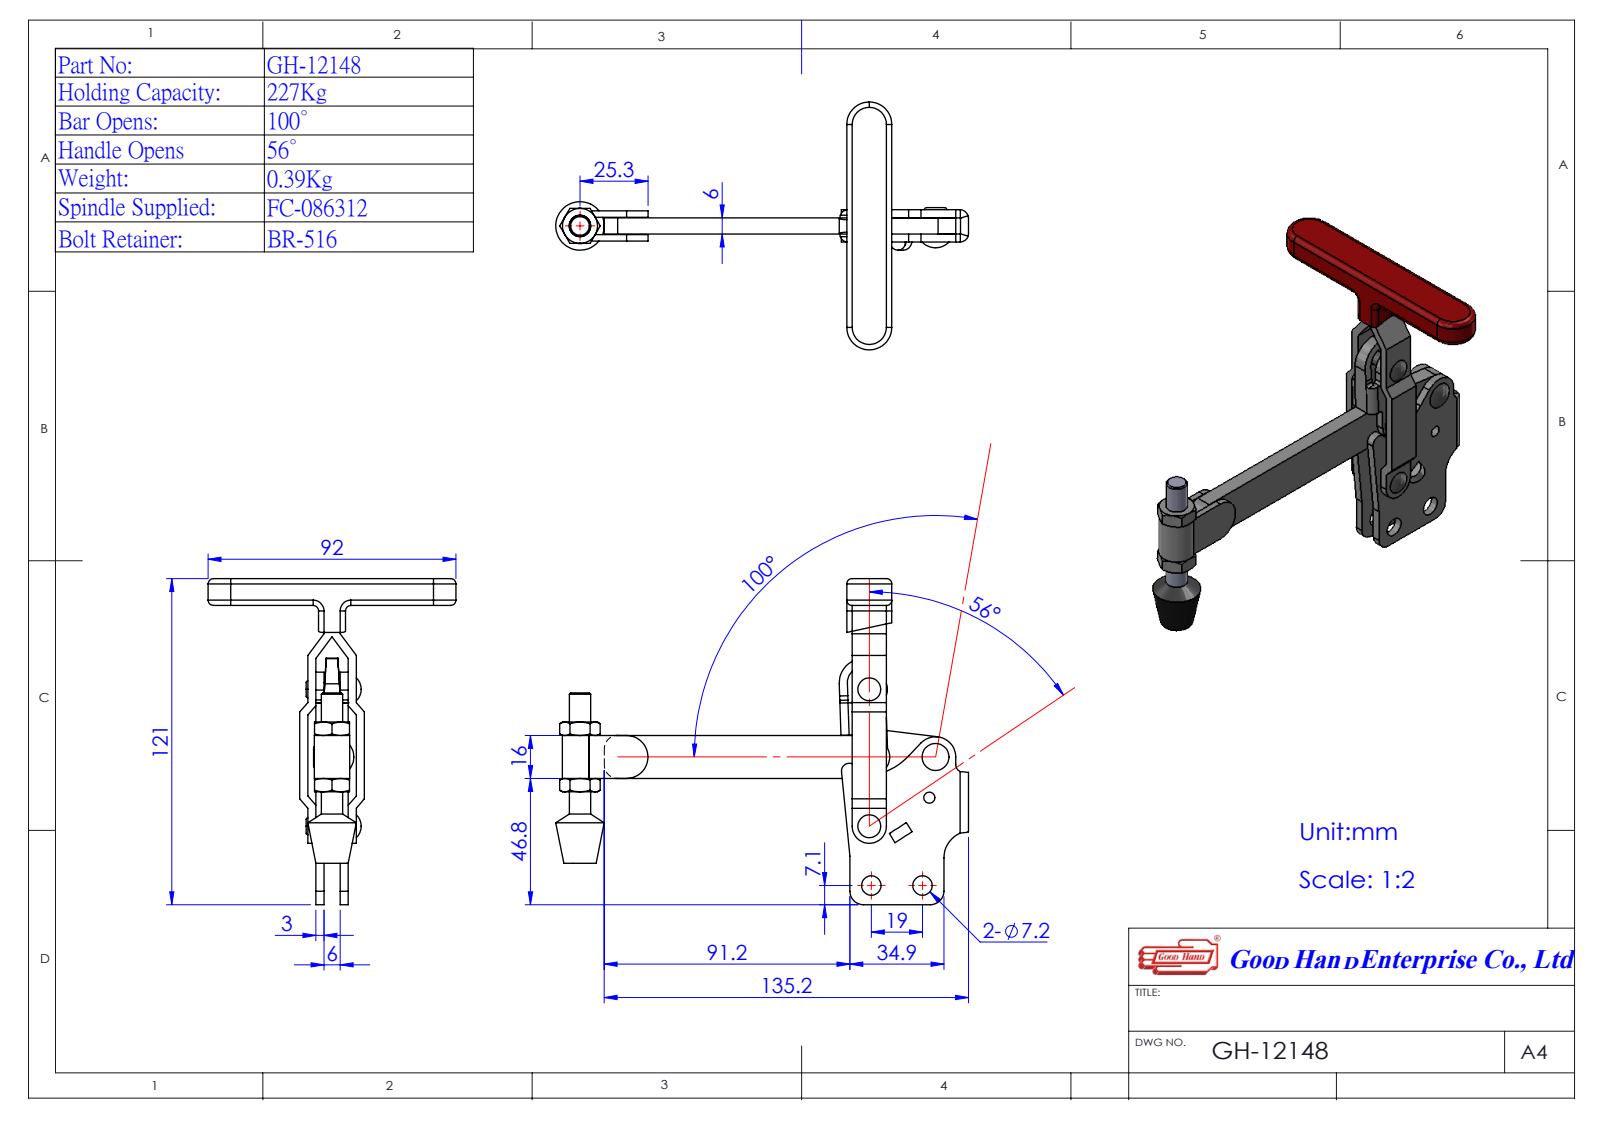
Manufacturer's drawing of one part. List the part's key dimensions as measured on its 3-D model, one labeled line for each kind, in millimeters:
Part name (STEP PRODUCT): GH-12148(簡化); 11214208-1^GH-12148(簡化); Group1^EMC12141; Group2^GH-12148(簡化) (+2 more)
STEP written by: SolidWorks 2016 (AUTOMOTIVE_DESIGN)
Units: millimetres
Bodies: 5 solids, 277 faces (133 planar, 93 cylindrical, 51 other)
Overall size (bounding box): 153.29 × 121 × 92
Volume: 61 295 mm³ · Surface area: 35 261 mm²
Round holes (diameter × count): ⌀4 ×3, ⌀7.2 ×2, ⌀4.5 ×1
Round bosses / shafts (diameter × count): ⌀7.93 ×1, ⌀4.5 ×1, ⌀4 ×1
Partial cylindrical surfaces — rounded edges, fillets, slot ends (radius × count): R5 ×4, R7.5 ×4, R0.1 ×2, R1 ×2, R2.42 ×2, R3 ×2, R3.1 ×2, R6.4 ×2
Main face-to-face distances: 3, 6, 9, 12, 15, 18, 10, 8.8, 2, 6.4
Hole centre spacings: 19, 22.01, 23.4, 25.13, 25.73, 29.56, 35.14, 35.58
